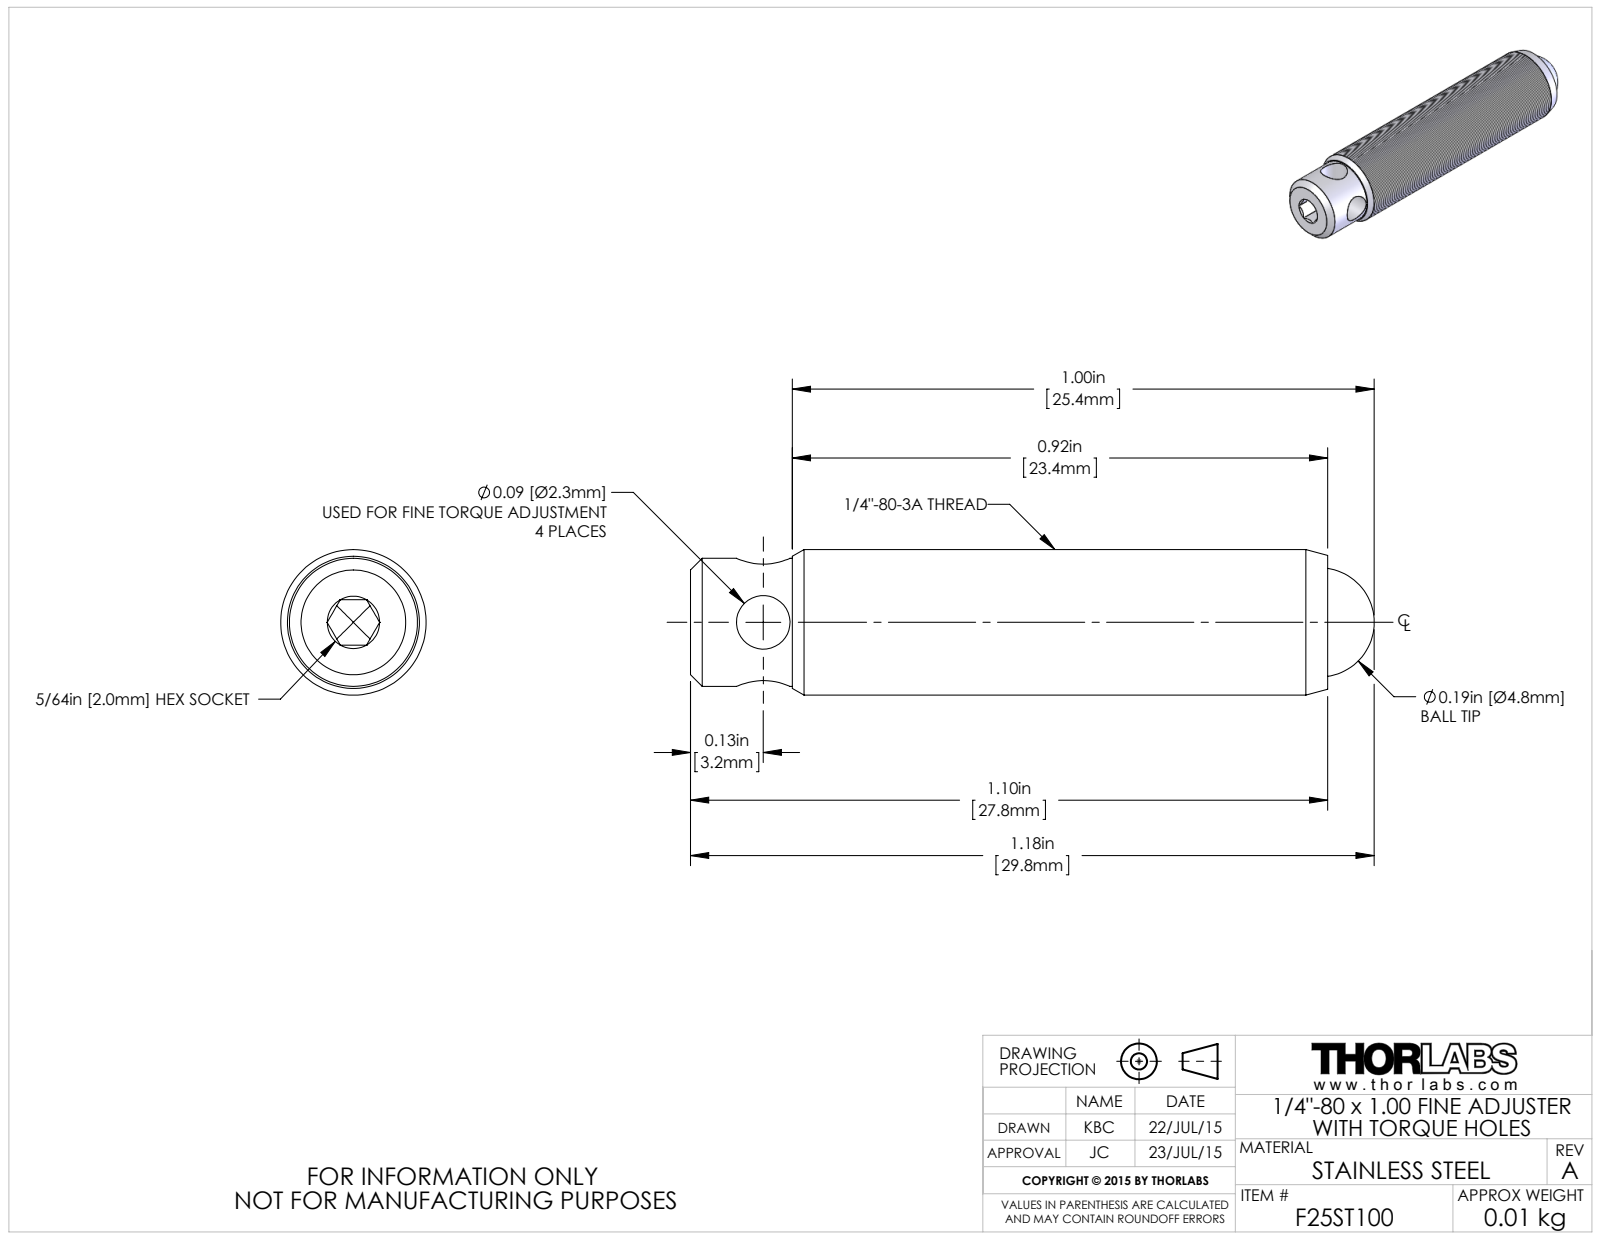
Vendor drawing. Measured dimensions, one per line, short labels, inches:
name: TTN045070-E0W
written by: SolidWorks 2014 (AUTOMOTIVE_DESIGN)
unit: in
bodies: 2 solids, 40 faces (9 planar, 14 cylindrical, 17 other)
size: 1.175 × 0.25 × 0.25
volume: 0.05 in³; area: 1.142 in²
holes: 2× ⌀0.092, 1× ⌀0.188
bosses: 1× ⌀0.25, 1× ⌀0.22
face distances: 1.095, 0.078, 0.175, 0.92
